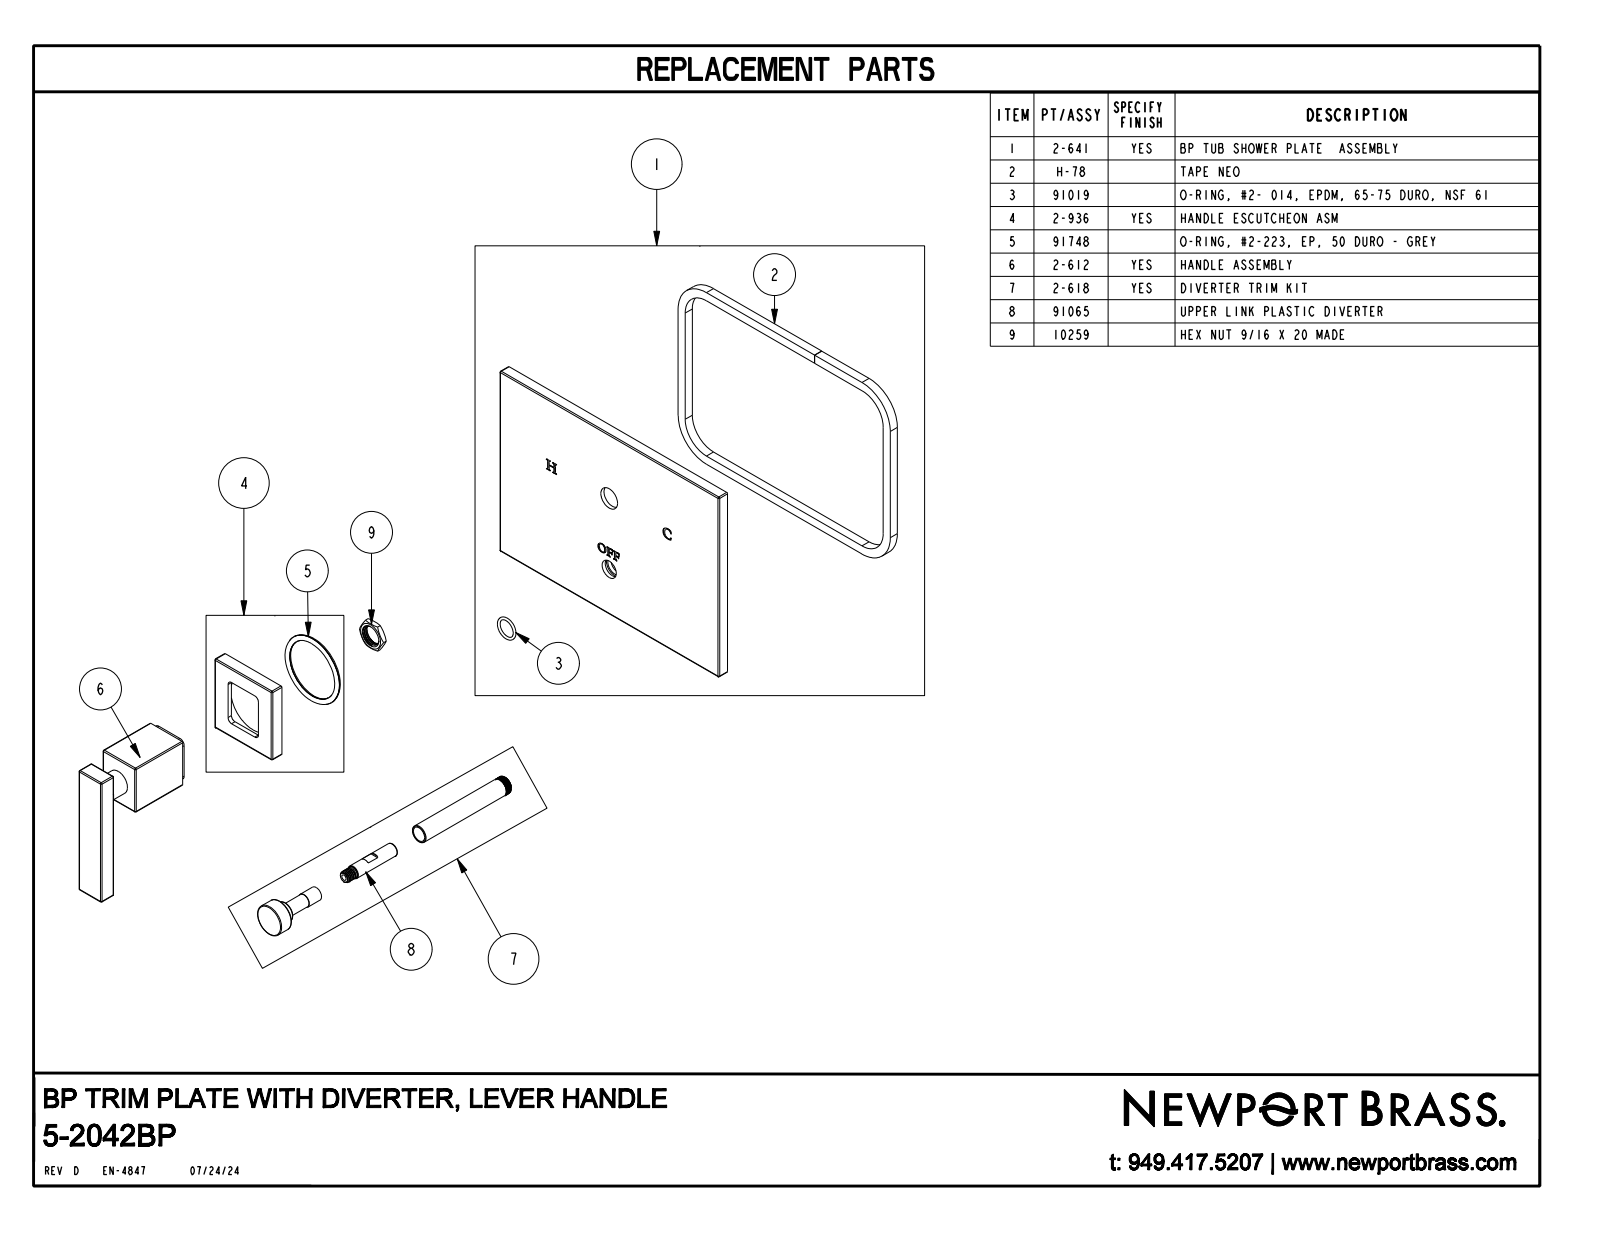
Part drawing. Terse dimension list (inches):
name: 5-2042BP
written by: CREO PARAMETRIC BY PTC INC, 2018400 (CONFIG_CONTROL_DESIGN)
unit: in
bodies: 1 solid, 325 faces (67 planar, 48 cylindrical, 210 other)
size: 7.75 × 5.5 × 3.36
volume: 19.1 in³; area: 117.2 in²
bosses: 1× ⌀0.84, 1× ⌀0.65, 1× ⌀0.54, 1× ⌀0.523, 1× ⌀0.354
rounds: 36× R0.03
face distances: 0.31, 3.295, 4.455, 3.475, 4.275, 0.18, 0.98, 3.36, 3.05, 2.7
